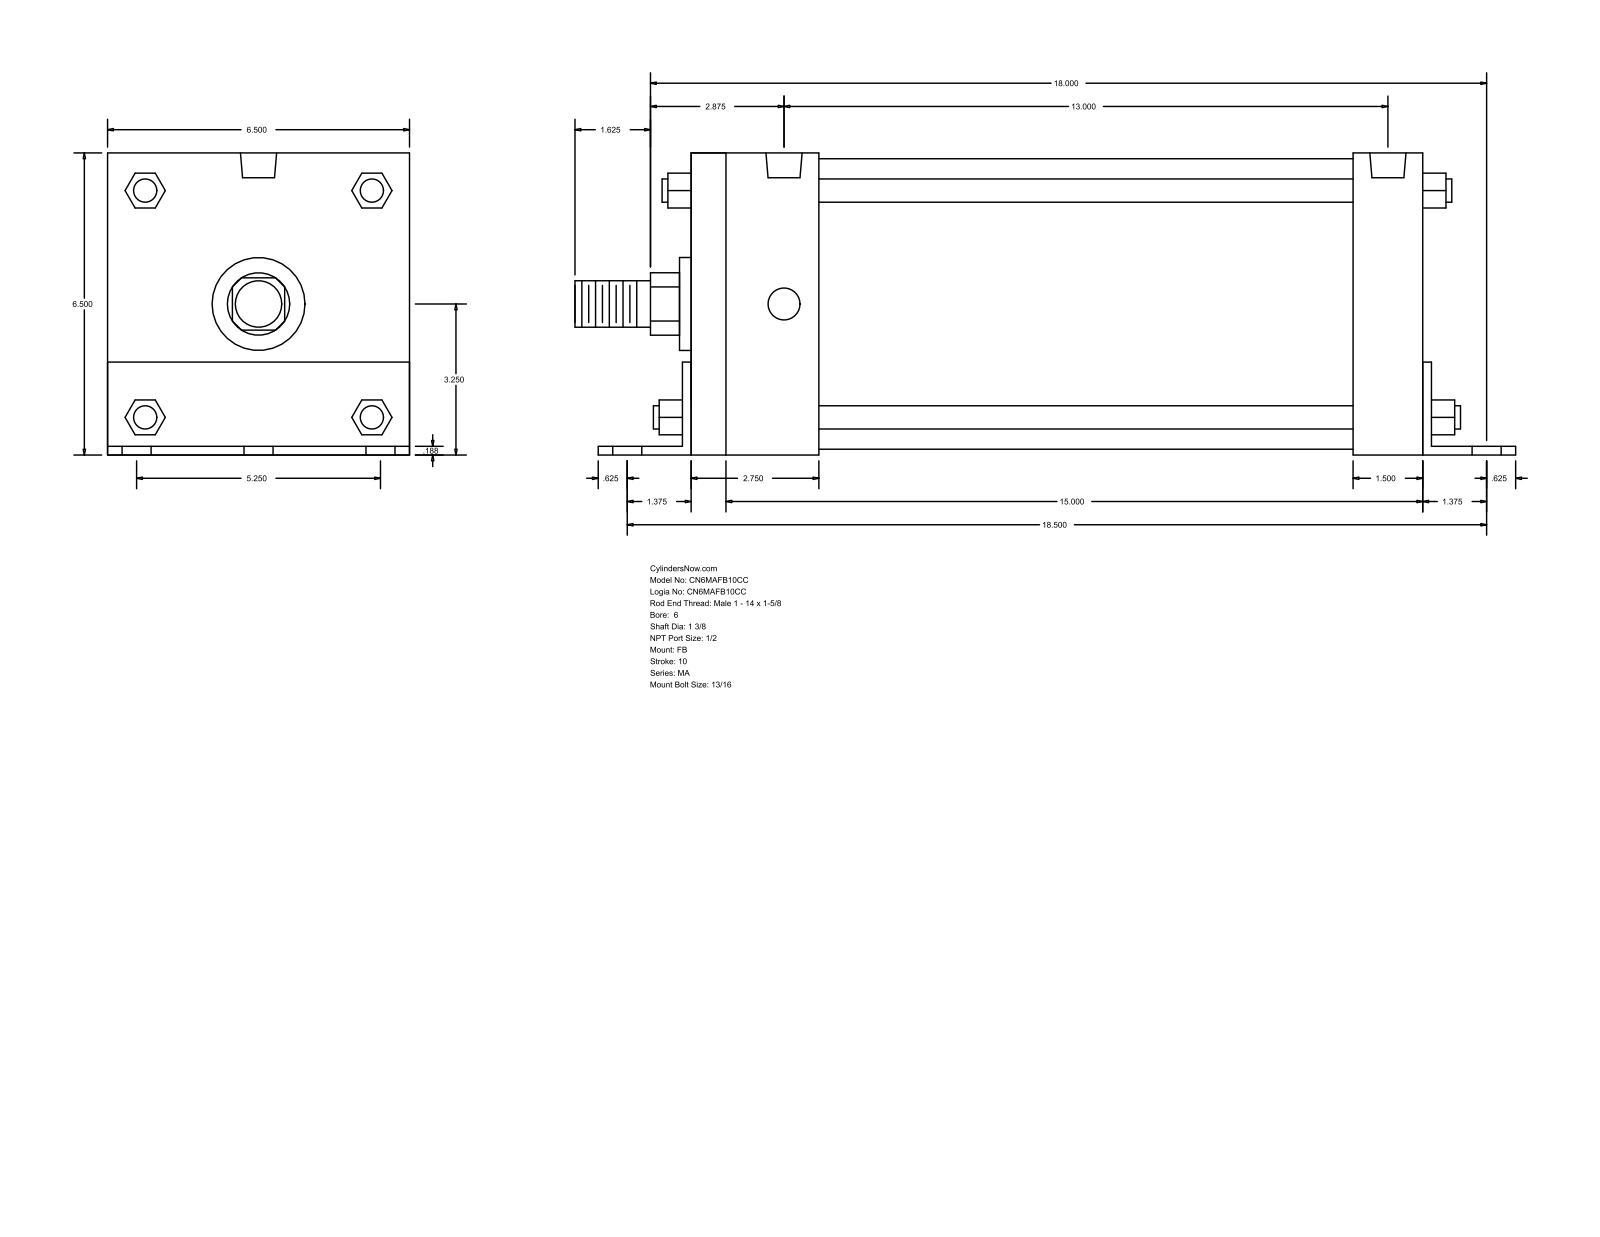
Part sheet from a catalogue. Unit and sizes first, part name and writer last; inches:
Units: inches
Overall size (bounding box): 20.125 × 6.502 × 6.5
Round holes (diameter × count): ⌀0.813 ×6, ⌀0.687 ×4, ⌀0.778 ×2
Round bosses / shafts (diameter × count): ⌀0.5 ×4, ⌀6.25 ×1, ⌀2 ×1, ⌀1.375 ×1, ⌀1 ×1
Partial cylindrical surfaces — rounded edges, fillets, slot ends (radius × count): R0.672 ×1, R1.262 ×1
Main face-to-face distances: 6.5, 0.187, 15.625, 6.502, 0.185, 6.315, 0.188, 1.5, 1.687, 16
Hole centre spacings: 2.625, 18.561, 18.375, 3.3, 3.377, 4.276, 5.25, 12.875
Bodies: 0 solids, 140 faces (105 planar, 35 cylindrical, 0 other)
Part name (STEP PRODUCT): MA_FB__0600_1.375
STEP written by: GSSL Pune (CONFIG_CONTROL_DESIGN)
